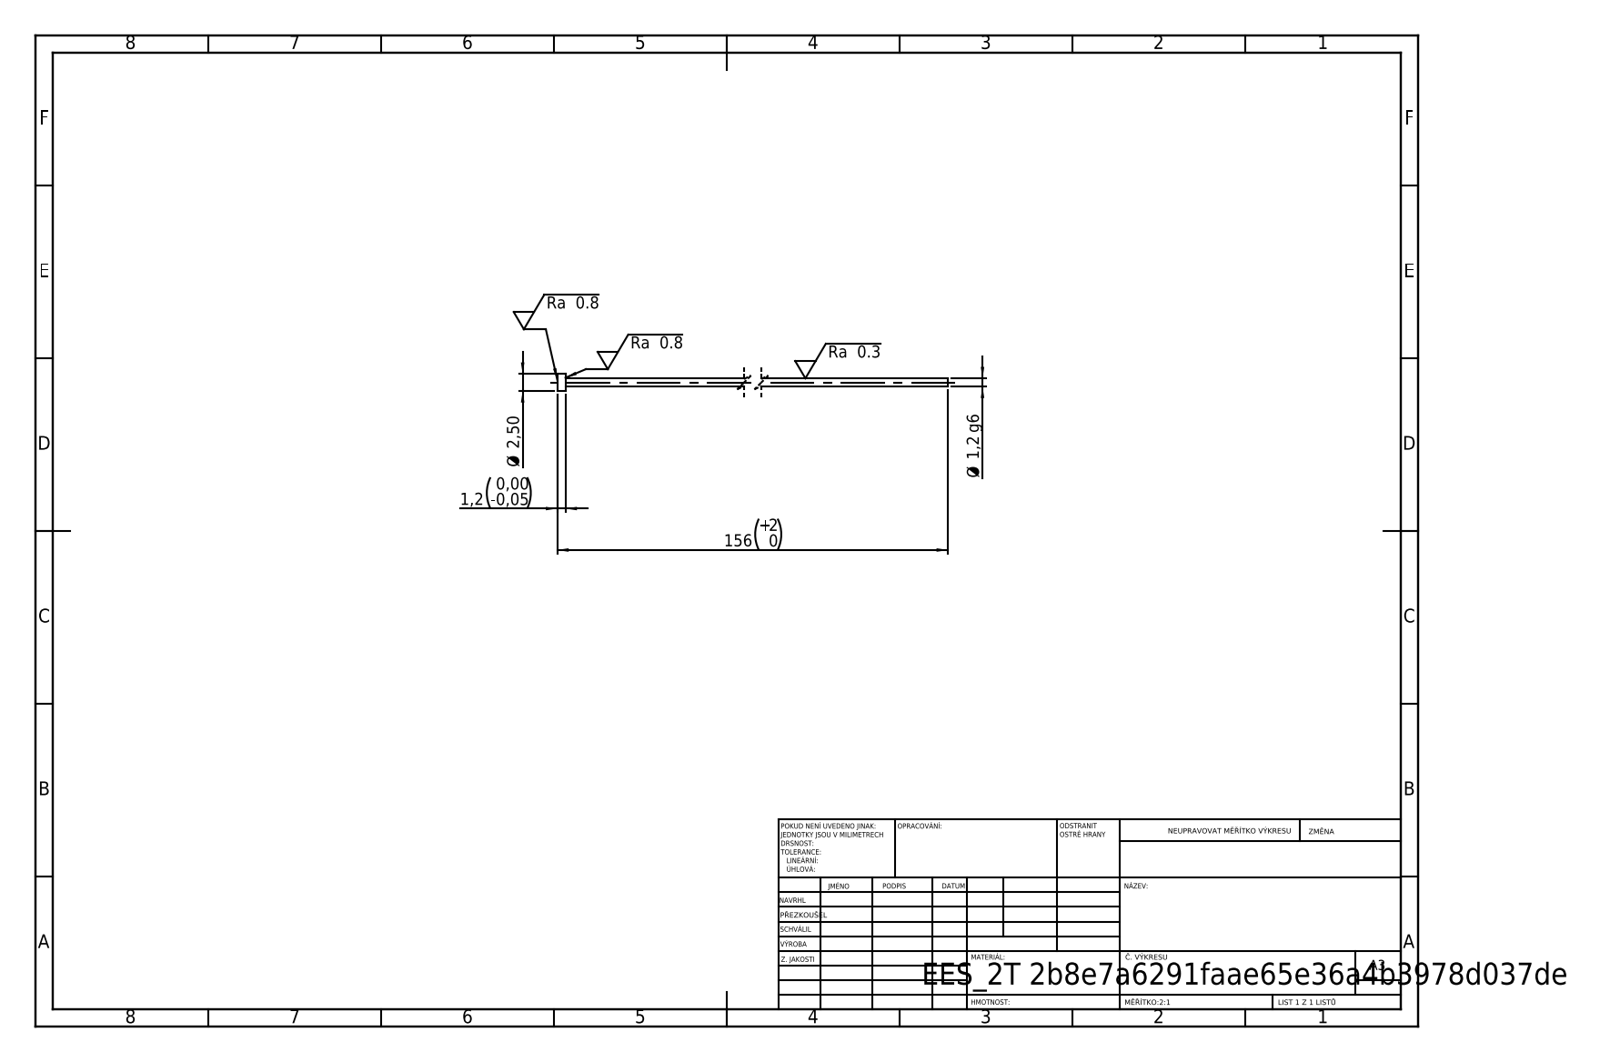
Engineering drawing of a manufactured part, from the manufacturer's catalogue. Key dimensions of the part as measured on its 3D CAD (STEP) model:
STEP written by: SolidWorks 2019 (CONFIG_CONTROL_DESIGN)
Units: millimetres
Bodies: 1 solid, 7 faces (3 planar, 4 cylindrical, 0 other)
Overall size (bounding box): 156 × 2.5 × 2.5
Volume: 181 mm³ · Surface area: 603 mm²
Round bosses / shafts (diameter × count): ⌀2.5 ×1, ⌀1.2 ×1
Main face-to-face distances: 1.2, 156, 154.8
